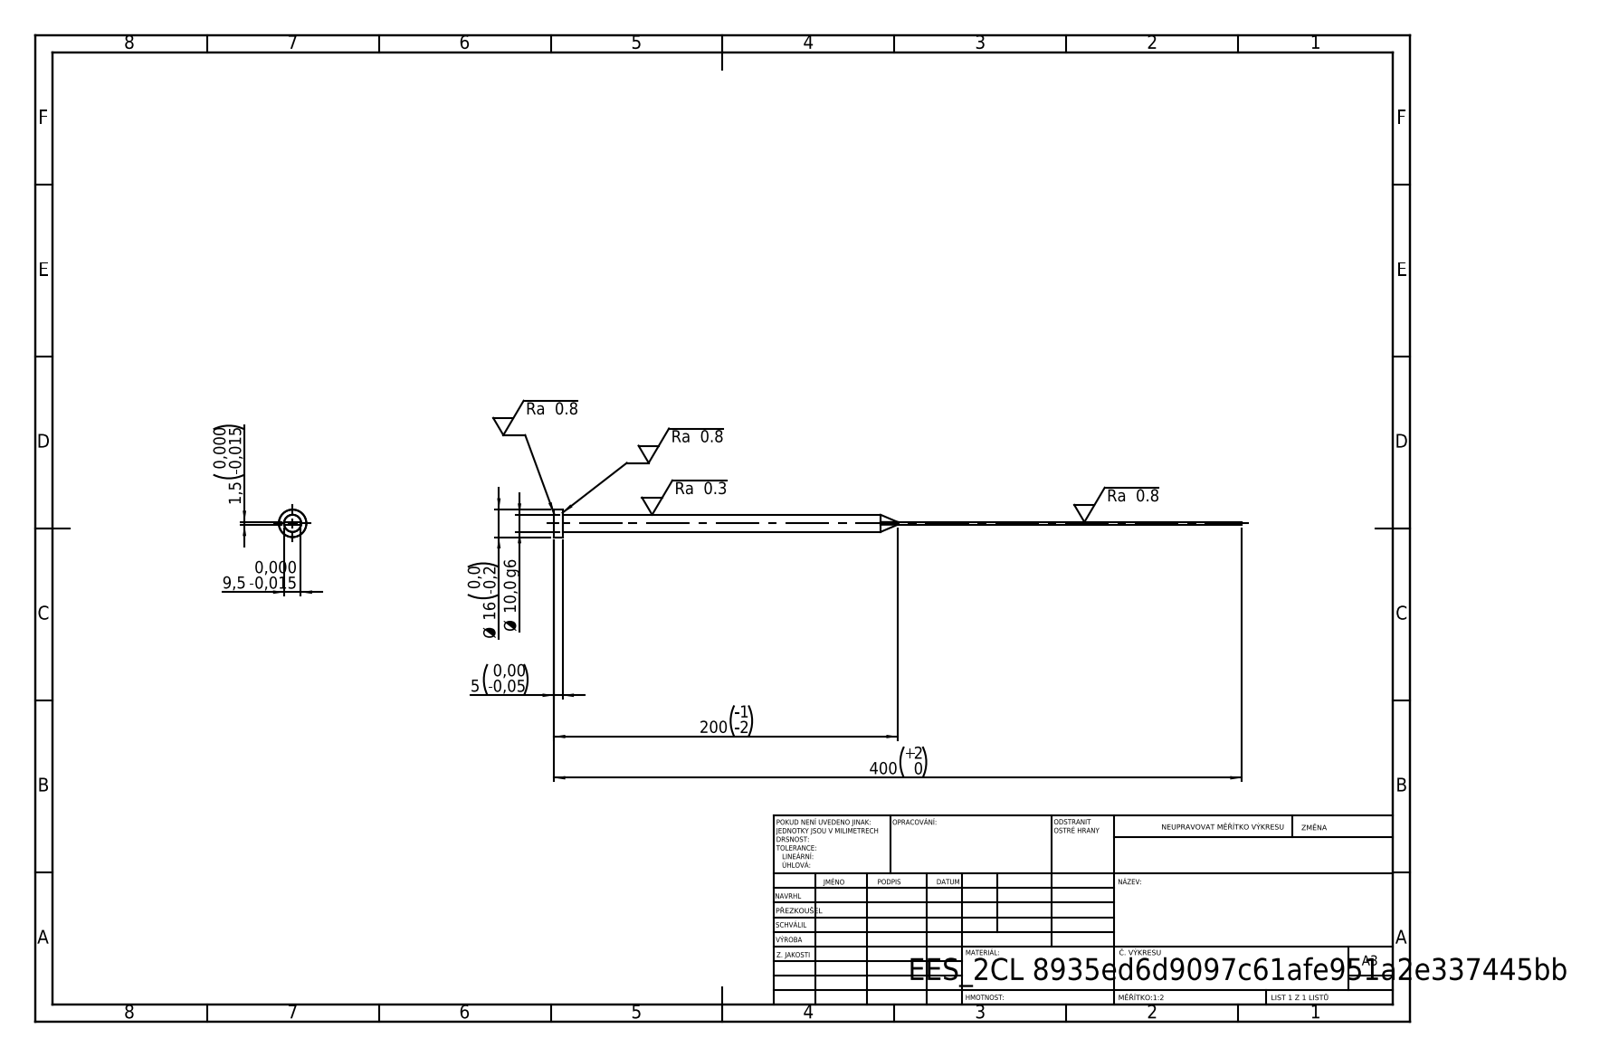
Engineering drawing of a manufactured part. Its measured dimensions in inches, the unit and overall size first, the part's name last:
Units: inches
Overall size (bounding box): 15.748 × 0.63 × 0.63
Round bosses / shafts (diameter × count): ⌀0.63 ×1, ⌀0.394 ×1
Main face-to-face distances: 0.059, 0.374, 0.197, 15.748, 15.551
Volume: 1.149 in³ · Surface area: 17.15 in²
Bodies: 1 solid, 15 faces (7 planar, 4 cylindrical, 4 other)
STEP written by: SolidWorks 2019 (CONFIG_CONTROL_DESIGN)
